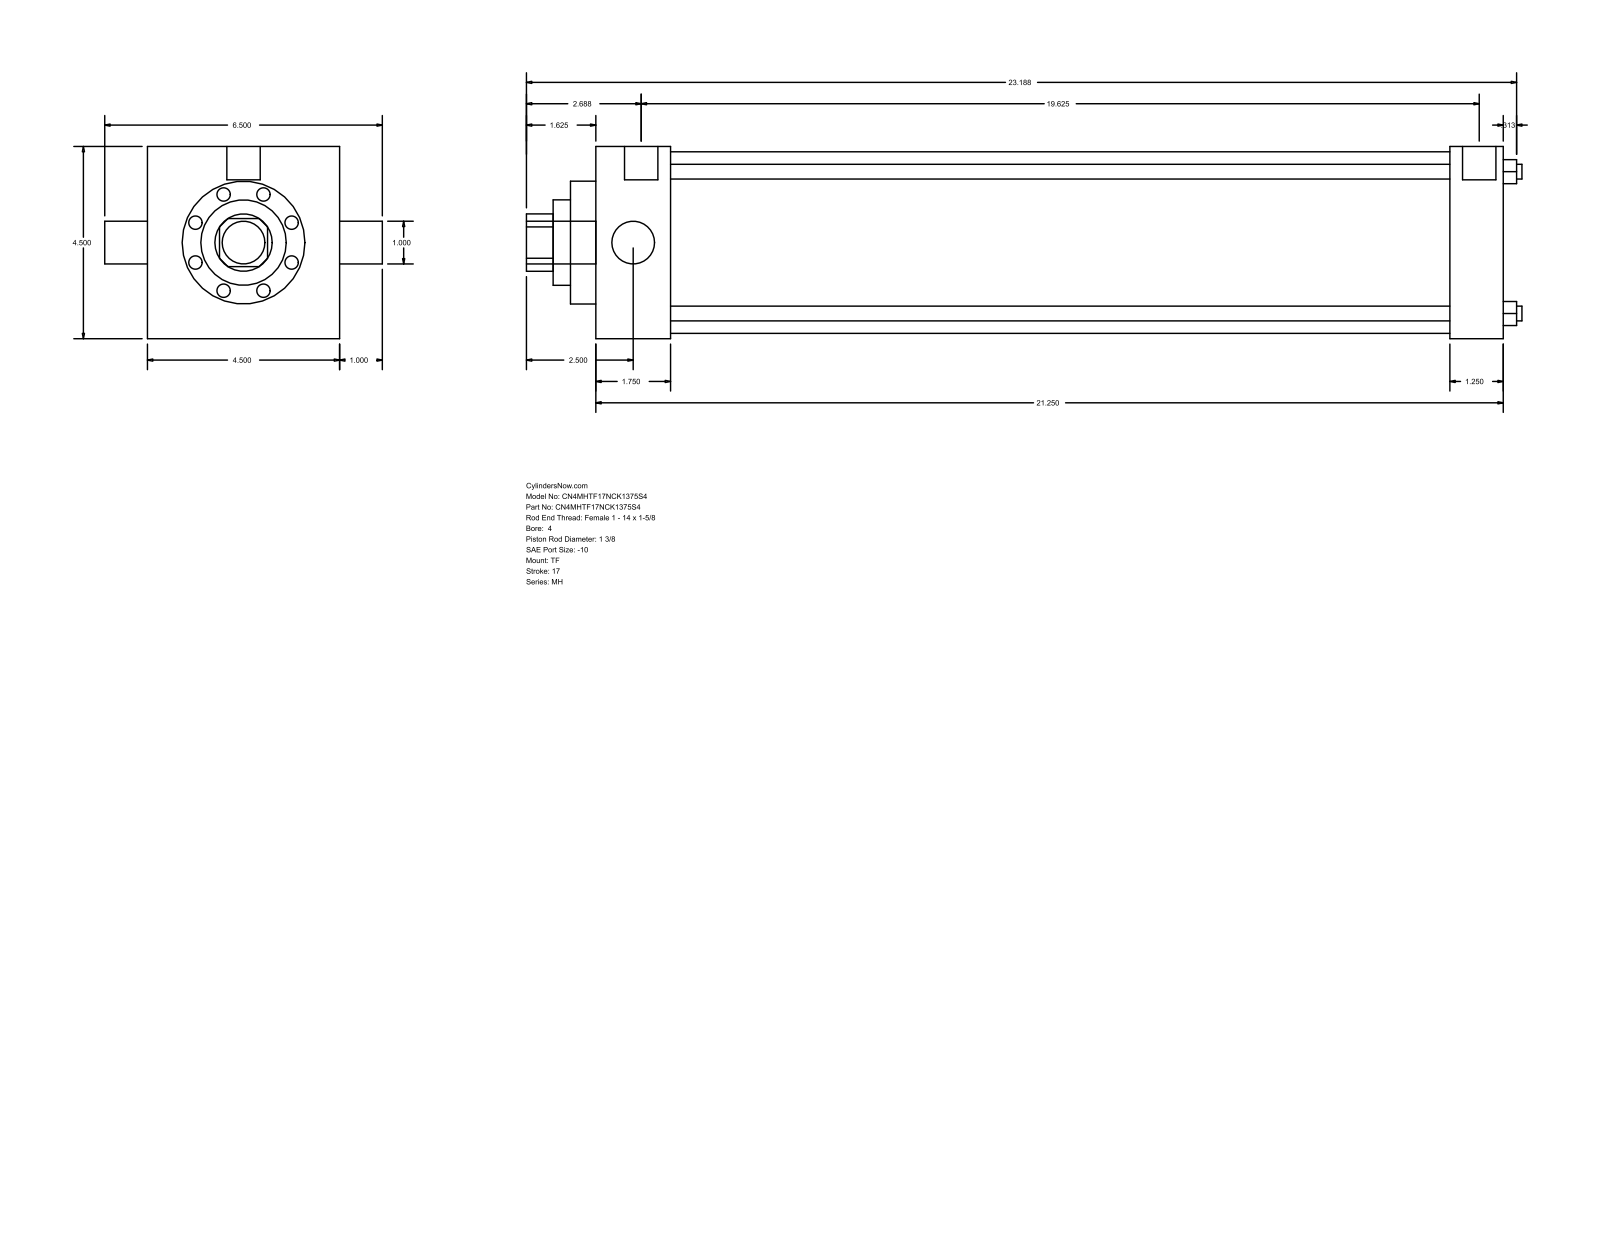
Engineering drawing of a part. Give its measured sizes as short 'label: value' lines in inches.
name: MH_TF__0400_1.375
written by: GSSL Pune (CONFIG_CONTROL_DESIGN)
unit: in
bodies: 0 solids, 86 faces (61 planar, 25 cylindrical, 0 other)
size: 23.313 × 6.5 × 4.5
holes: 4× ⌀0.345, 1× ⌀1, 1× ⌀1.375, 1× ⌀2, 1× ⌀2.875, 1× ⌀4.25
bosses: 3× ⌀0.344, 2× ⌀0.781, 1× ⌀1
rounds: 1× R0.672
face distances: 4.5, 21.25, 1.75, 19.5, 20, 18.25, 1.25, 0.594, 2.344, 20.594
hole spacings: 2.347, 3.32, 4.695
